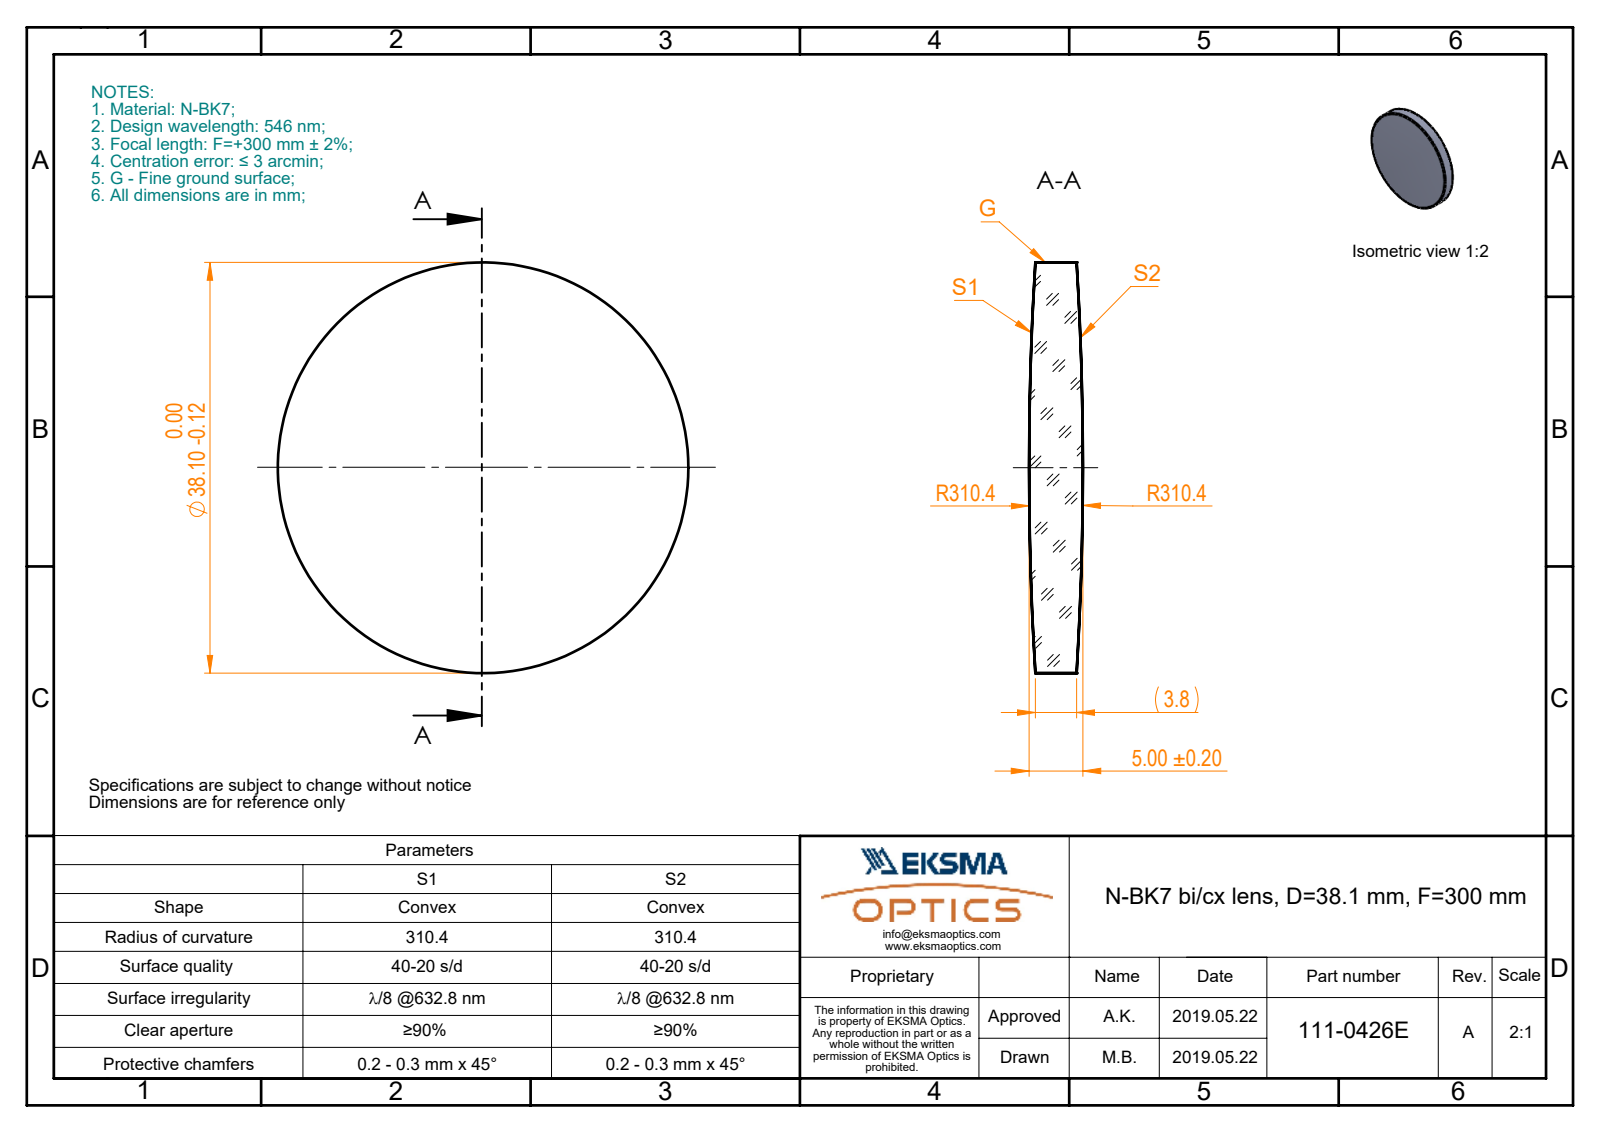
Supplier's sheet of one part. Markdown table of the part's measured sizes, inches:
| quantity | value |
| --- | --- |
| part name | 111-0426E BK7 bi-cx 38.1 F300 |
| STEP written by | SolidWorks 2017 (CONFIG_CONTROL_DESIGN) |
| units | inches |
| bodies | 1 solid, 6 faces (0 planar, 2 cylindrical, 4 other) |
| overall size | 1.5 × 1.5 × 0.197 |
| volume | 0.307 in³ |
| surface area | 4.249 in² |
| round bosses / shafts (diameter × count) | 1.5 × 1 |
